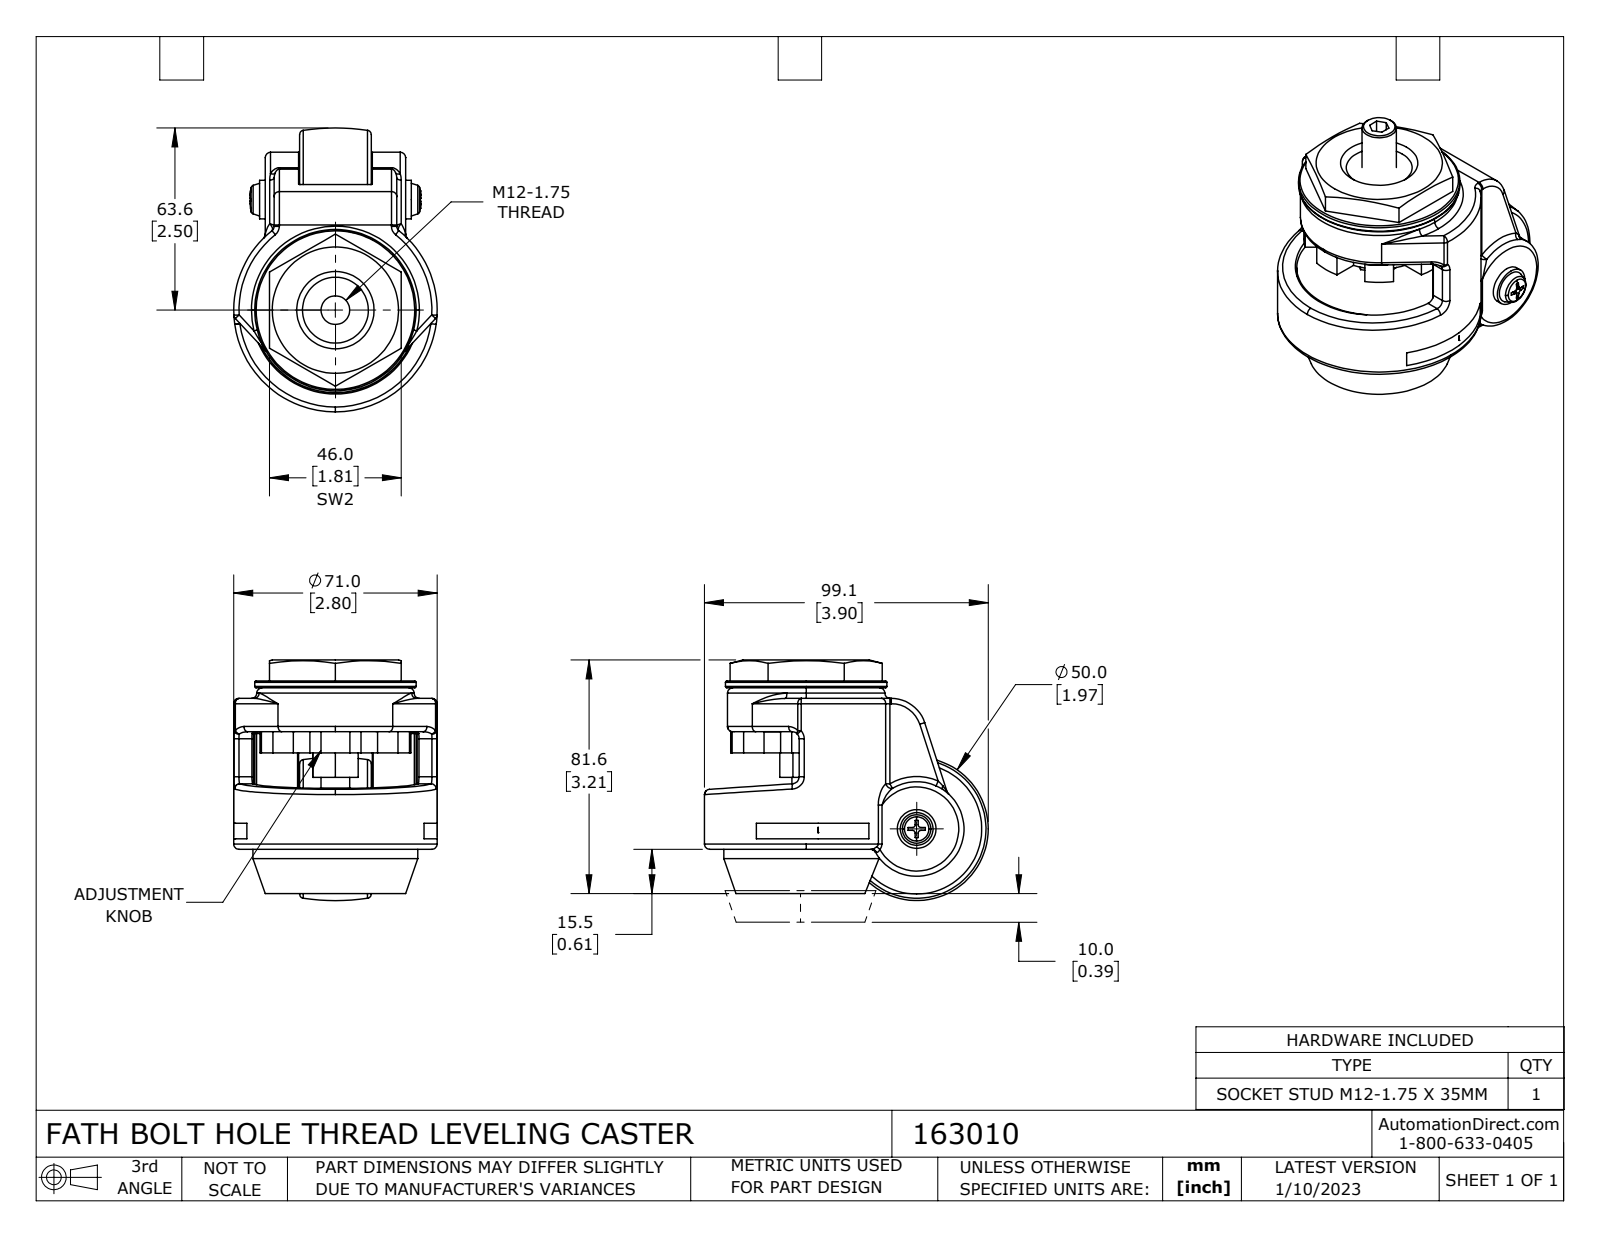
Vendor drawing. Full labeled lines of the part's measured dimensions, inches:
Part name (STEP PRODUCT): 163010
STEP written by: SolidWorks 2021 (CONFIG_CONTROL_DESIGN)
Units: inches
Bodies: 2 solids, 316 faces (108 planar, 101 cylindrical, 107 other)
Overall size (bounding box): 3.917 × 3.902 × 2.797
Volume: 16.06 in³ · Surface area: 83.39 in²
Round holes (diameter × count): ⌀0.394 ×1, ⌀0.405 ×1, ⌀2.305 ×1
Round bosses / shafts (diameter × count): ⌀2.266 ×1, ⌀2.218 ×1, ⌀0.531 ×1, ⌀0.472 ×1, ⌀0.315 ×1
Partial cylindrical surfaces — rounded edges, fillets, slot ends (radius × count): R0.072 ×18, R0.024 ×16, R0.039 ×4, R0.023 ×2, R0.096 ×2, R0.241 ×2, R0.482 ×1, R0.651 ×1
Main face-to-face distances: 0.014, 0.998, 1.446, 0.984, 1.935, 0.489, 0.458, 0.472, 1.457, 1.471
